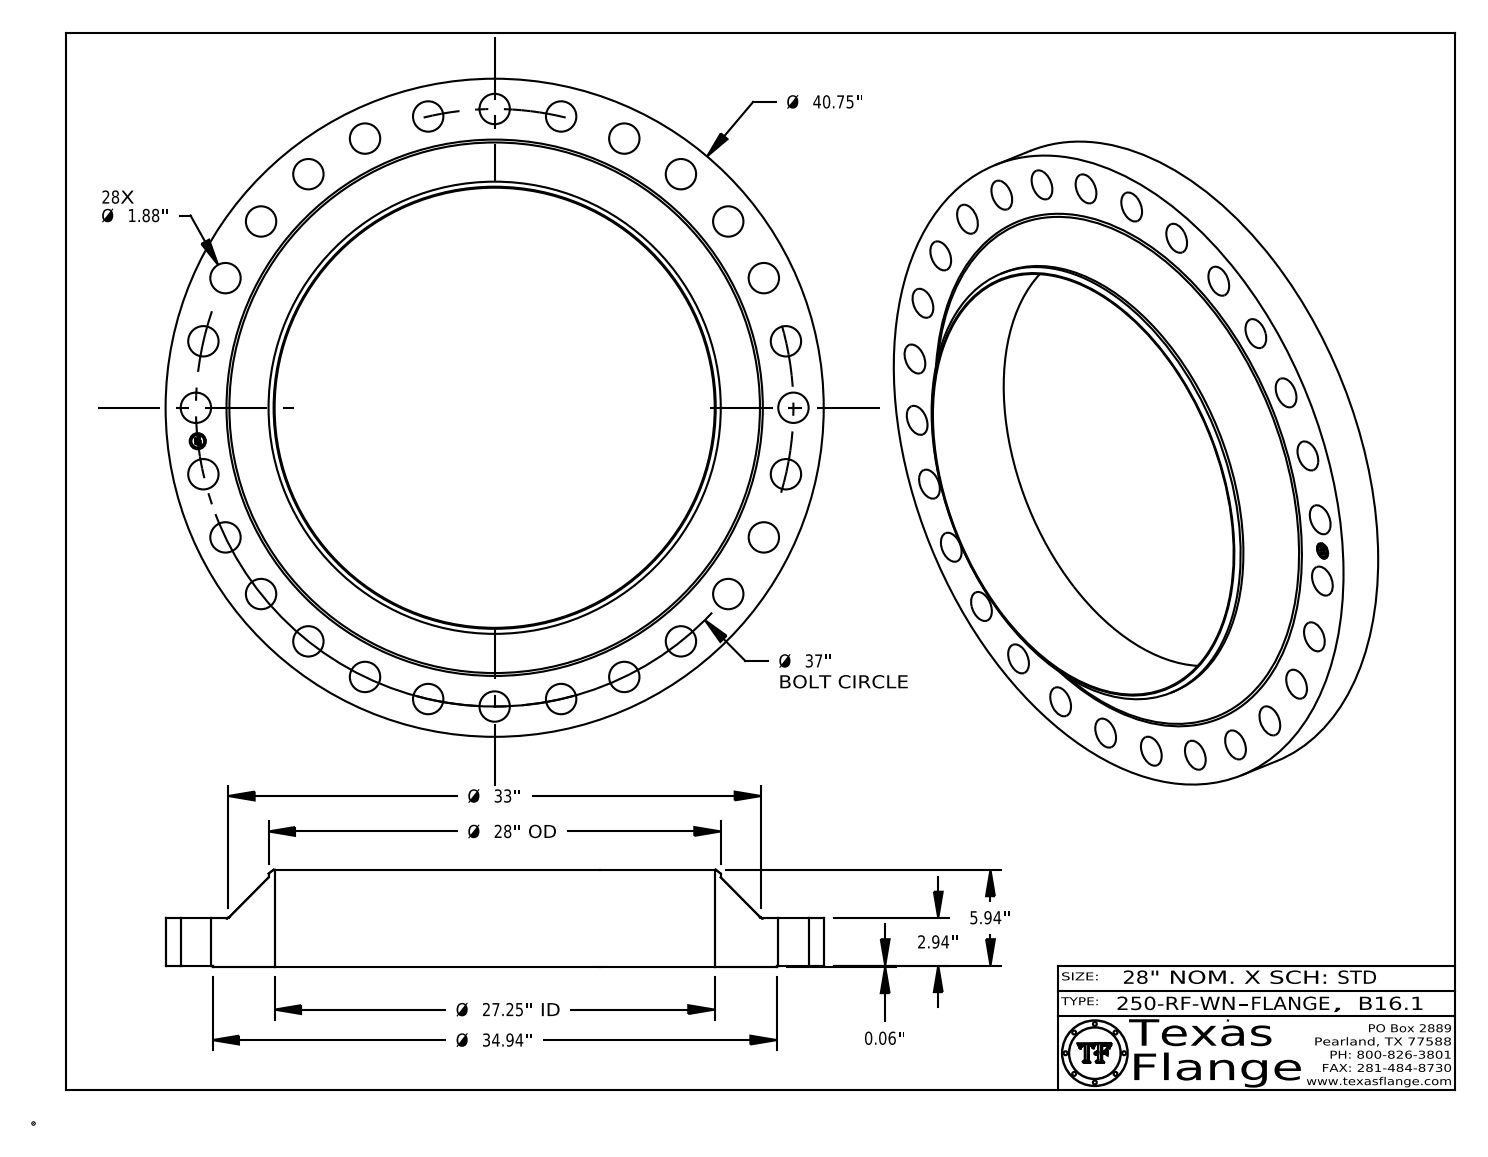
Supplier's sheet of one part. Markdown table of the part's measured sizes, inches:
| quantity | value |
| --- | --- |
| part name | 250-RF-WN, B16.1 |
| STEP written by | CATIA V5 STEP AP203 (CONFIG_CONTROL_DESIGN) |
| units | inches |
| bodies | 1 solid, 459 faces (369 planar, 84 cylindrical, 6 other) |
| overall size | 40.75 × 40.75 × 6.002 |
| volume | 2 303 in³ |
| surface area | 2 798 in² |
| round holes (diameter × count) | 1.88 × 28, 1 × 1, 27.25 × 1 |
| round bosses / shafts (diameter × count) | 0.061 × 8, 40.75 × 1, 34.94 × 1, 28 × 1, 0.788 × 1 |
| main face-to-face distances | 3.003, 0.063, 2.94, 6.003, 5.94, 3, 0.015, 2.988, 2.925, 3.015 |
| hole center spacings | 18.5, 26.163, 31.329, 36.072, 36.767, 33.336, 4.143, 16.054 |
